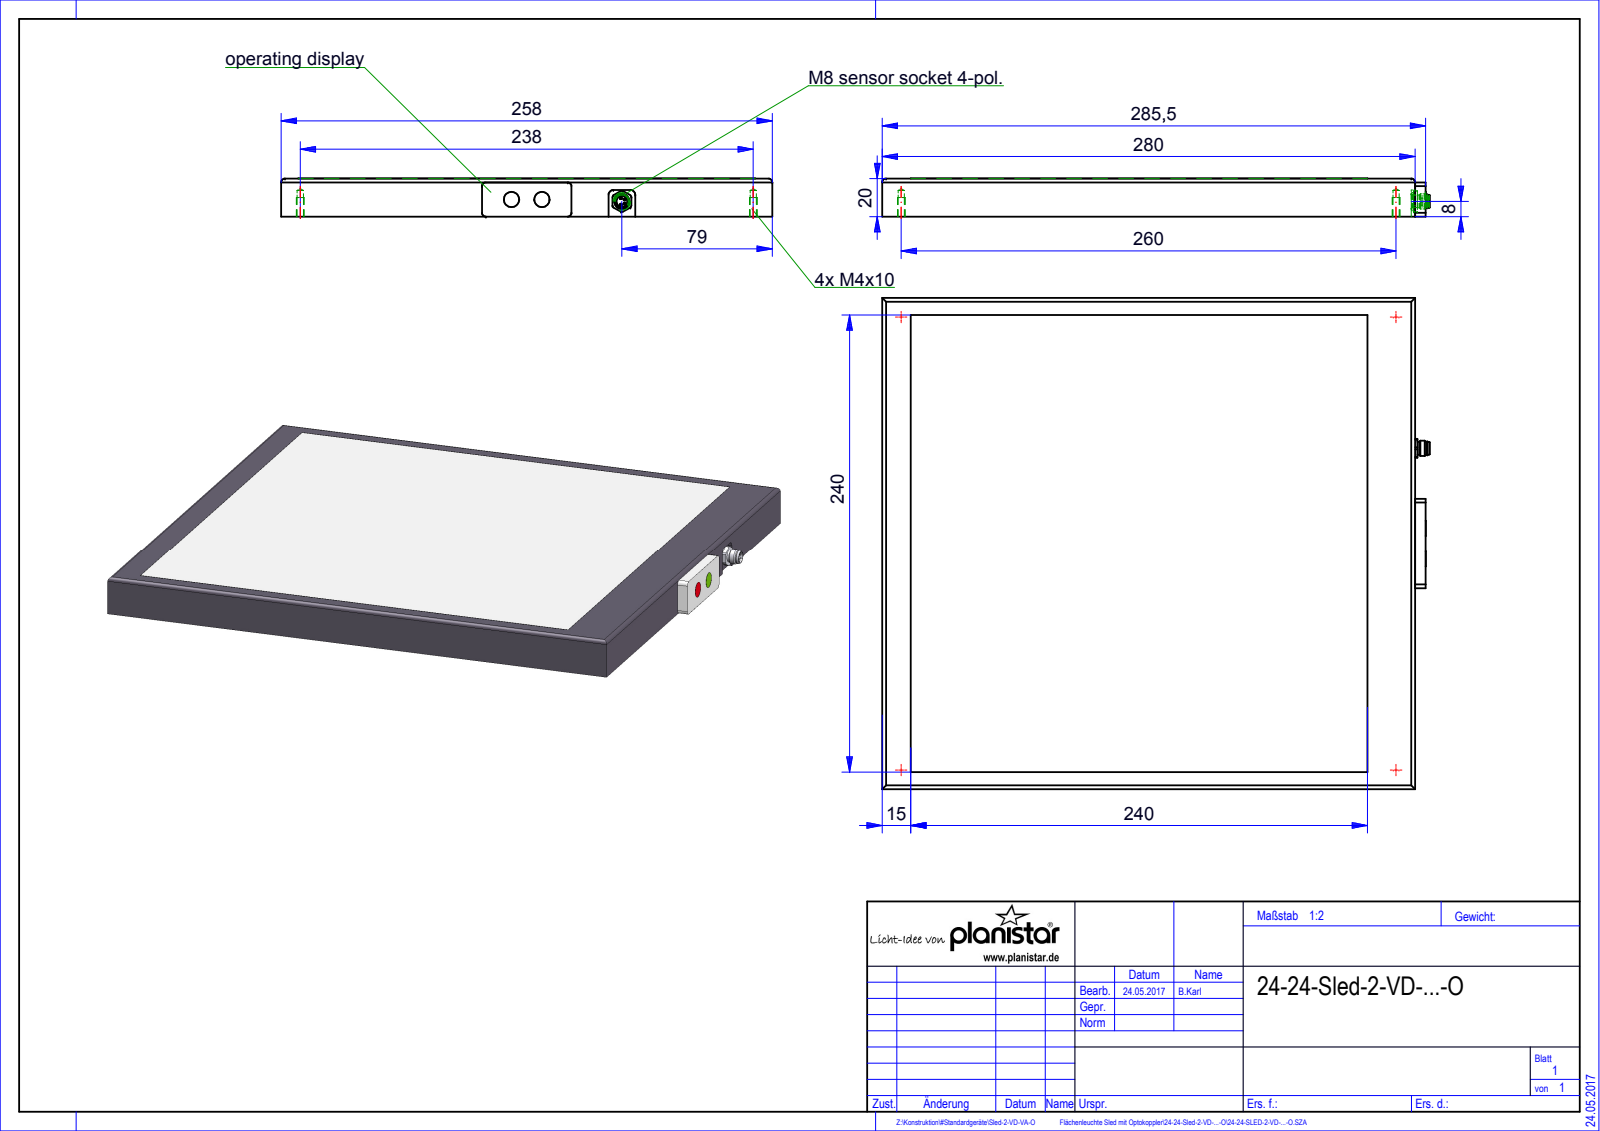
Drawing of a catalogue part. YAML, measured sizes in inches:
part_name: "Root; Baugruppe_Xled-2-VD; QUADER_0; 09-3391-00-04"
step_written_by: "HiCAD 2015 2002.1 Build 408 (AUTOMOTIVE_DESIGN)"
units: inches
bodies: {solids: 3, faces: 89, planar: 39, cylindrical: 37, other: 13}
overall_size: [11.327, 10.157, 0.791]
volume: 88.73
surface_area: 261.8
round_holes:
  - {diameter: 0.13, count: 4}
  - {diameter: 0.157, count: 4}
  - {diameter: 0.228, count: 1}
round_bosses_or_shafts:
  - {diameter: 0.039, count: 4}
  - {diameter: 0.315, count: 3}
  - {diameter: 0.283, count: 1}
  - {diameter: 0.268, count: 1}
  - {diameter: 0.252, count: 1}
partial_cylinders:
  - {radius: 0.079, count: 8}
  - {radius: 0.098, count: 2}
  - {radius: 0.217, count: 1}
face_to_face_distances: [0.791, 0.787, 10.157, 11.024, 11.24, 0.217, 0.079, 0.083, 0.709, 10.945]
hole_center_spacings: [9.37, 10.236, 13.877]
